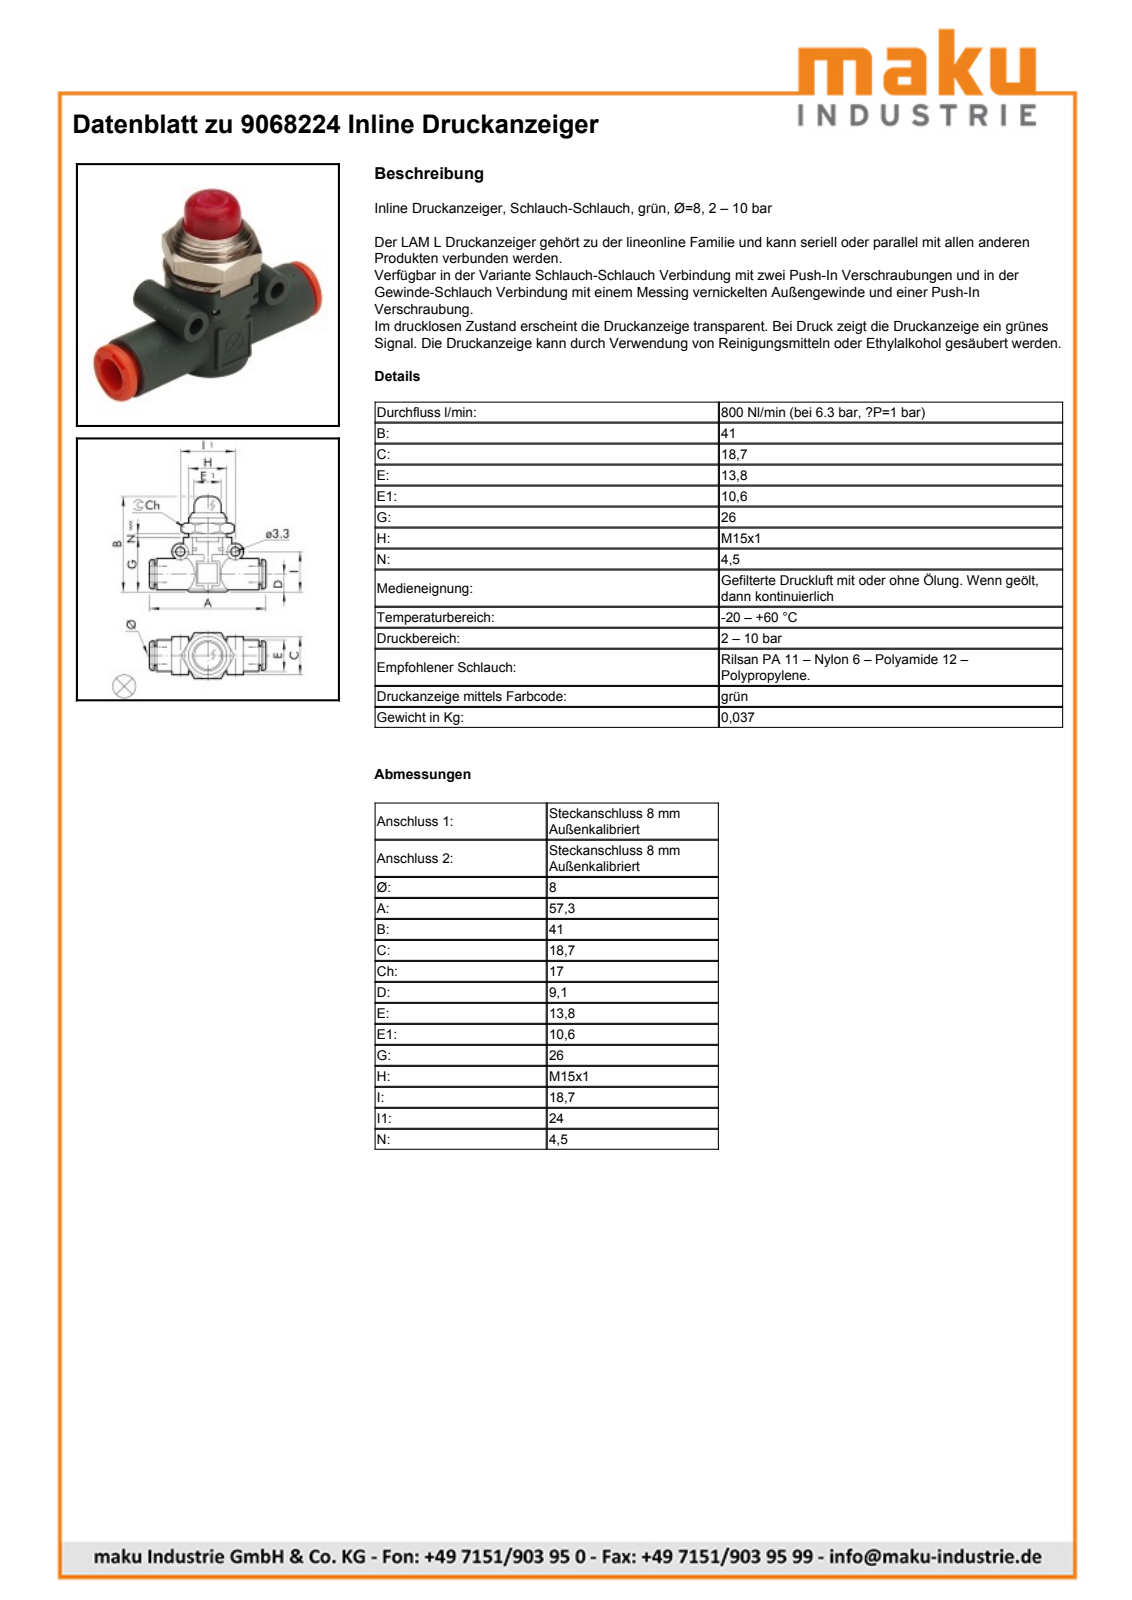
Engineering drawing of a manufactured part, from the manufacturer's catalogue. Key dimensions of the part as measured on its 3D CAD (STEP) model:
Part name (STEP PRODUCT): 9068224; LINE-ON-LINE D8 V2v/V3V_L body; LINE-ON-LINE D8 VNR-L bushing; LINE-ON-LINE D8 LAM-L plated
STEP written by: PARTsolutions (AUTOMOTIVE_DESIGN)
Units: millimetres
Bodies: 4 solids, 178 faces (103 planar, 53 cylindrical, 22 other)
Overall size (bounding box): 57.3 × 41 × 18.7
Volume: 9 454 mm³ · Surface area: 9 861 mm²
Round holes (diameter × count): ⌀3.3 ×2, ⌀6 ×2, ⌀5.5 ×1, ⌀8.1 ×1, ⌀11 ×1, ⌀11.65 ×1, ⌀12.5 ×1, ⌀15 ×1
Round bosses / shafts (diameter × count): ⌀6 ×2, ⌀18.8 ×1, ⌀14 ×1, ⌀13.8 ×1, ⌀13.6 ×1, ⌀10.6 ×1, ⌀9.5 ×1, ⌀9.2 ×1
Partial cylindrical surfaces — rounded edges, fillets, slot ends (radius × count): R3.75 ×1, R9.65 ×1, R10.2 ×1, R10.35 ×1, R11.45 ×1
Main face-to-face distances: 1.9, 24.1, 4.1, 20, 26, 21.9, 1.75, 17.45, 15.55, 37.95
Hole centre spacings: 15.37, 24
